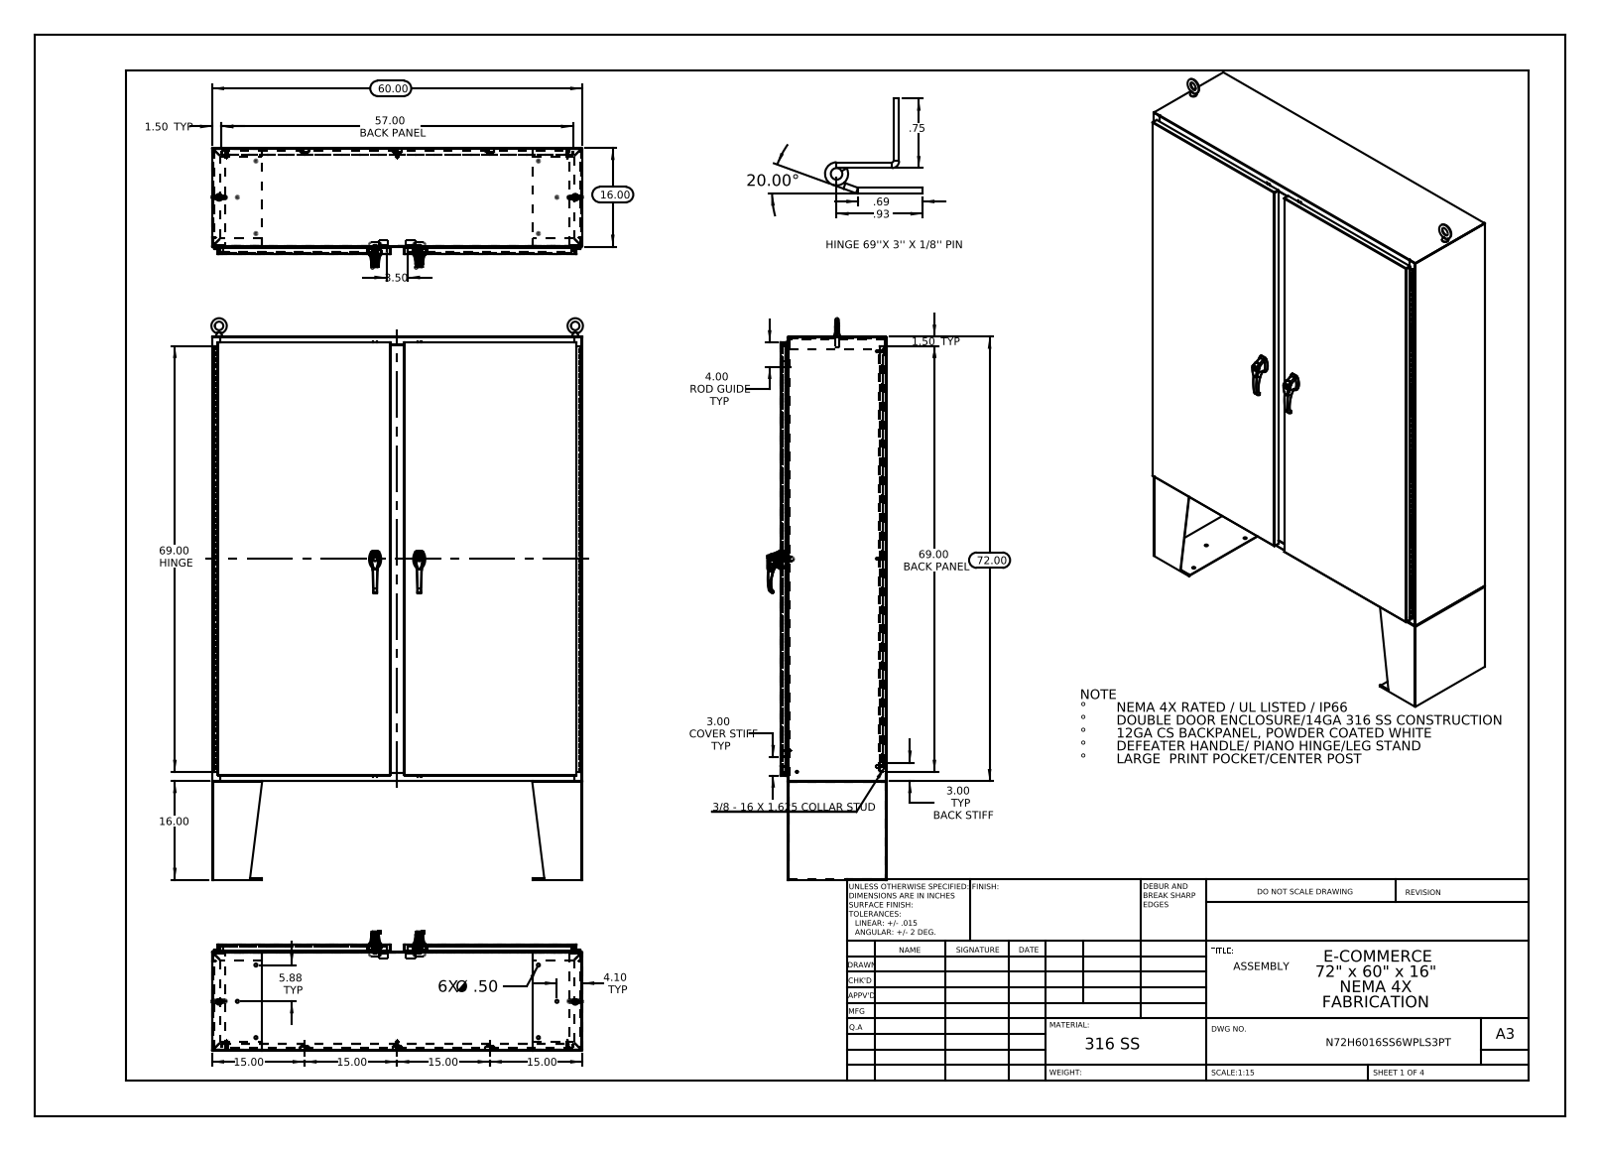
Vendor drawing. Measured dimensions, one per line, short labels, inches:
name: 2616310101; N72H6016SSWPLS3PT DD_Leg Kit; 00005309_G26103101; N72H6016SSWPLS3PT Eye-Bolt_Stiffener (+8 more)
written by: SolidWorks 2013 (CONFIG_CONTROL_DESIGN)
unit: in
bodies: 82 solids, 7496 faces (3026 planar, 3010 cylindrical, 1460 other)
size: 91 × 60.226 × 19.307
volume: 1 731 in³; area: 42 026 in²
holes: 20× ⌀0.25, 14× ⌀0.5, 6× ⌀0.138, 6× ⌀0.161, 4× ⌀0.079, 4× ⌀0.313, 4× ⌀0.437, 4× ⌀0.75, 2× ⌀0.125, 2× ⌀0.125, 2× ⌀0.197, 2× ⌀0.203
bosses: 12× ⌀0.157, 12× ⌀0.14, 10× ⌀0.625, 8× ⌀0.375, 8× ⌀0.33, 5× ⌀0.315, 5× ⌀0.236, 2× ⌀1.181
rounds: 72× R0.118, 66× R0.006, 46× R0.013, 38× R0.088, 28× R0.039, 24× R0.028, 12× R0.008, 12× R0.02
face distances: 0.075, 17.126, 0.104, 17.051, 1.075, 1, 16.051, 1.179, 1.104, 15.947
hole spacings: 7.152, 29.365, 0.295, 0.625, 0.841, 1.313, 1.561, 7.156
